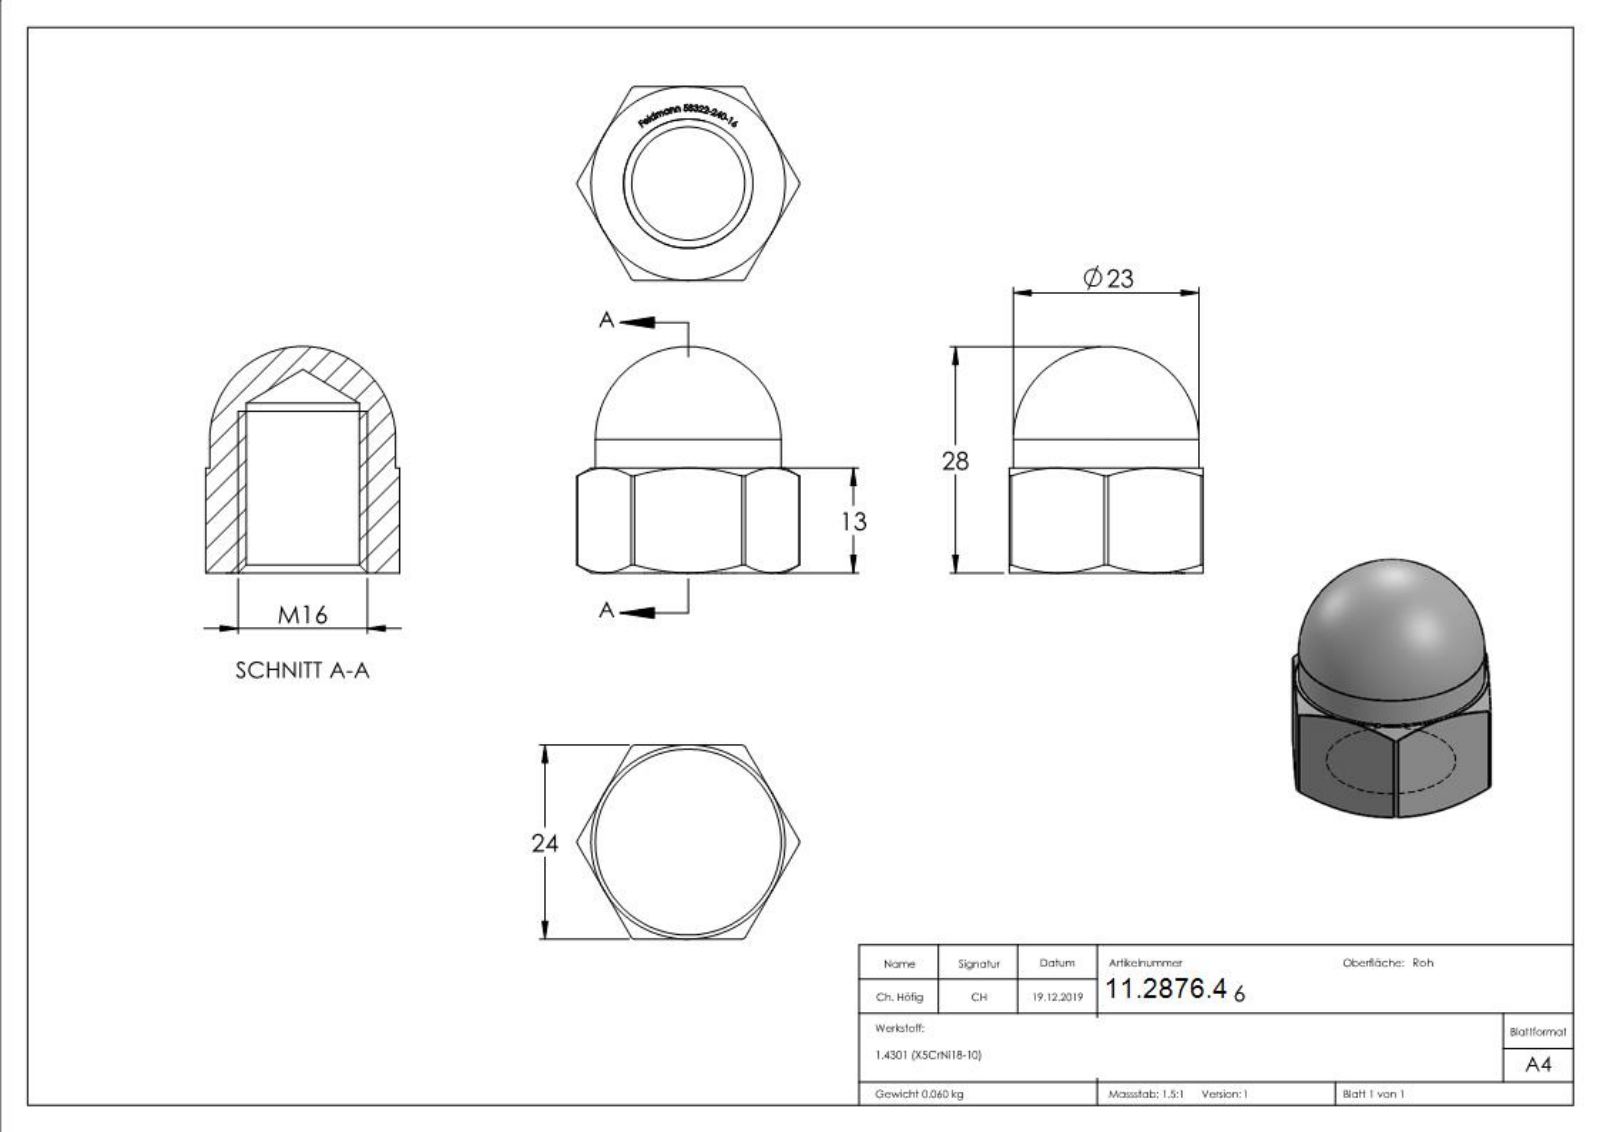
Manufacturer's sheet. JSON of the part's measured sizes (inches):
{"part_name": "58322-240-16", "step_written_by": "SolidWorks 2015 (CONFIG_CONTROL_DESIGN)", "units": "inches", "bodies": {"solids": 1, "faces": 31, "planar": 8, "cylindrical": 8, "other": 15}, "overall_size": [1.299, 1.085, 0.945], "volume_in3": 0.465, "surface_area_in2": 5.613, "round_holes": [[0.551, 1]], "round_bosses_or_shafts": [[0.906, 1]], "partial_cylinders_radius": [[0.02, 6]], "face_to_face_distances": [0.945, 0.512]}
